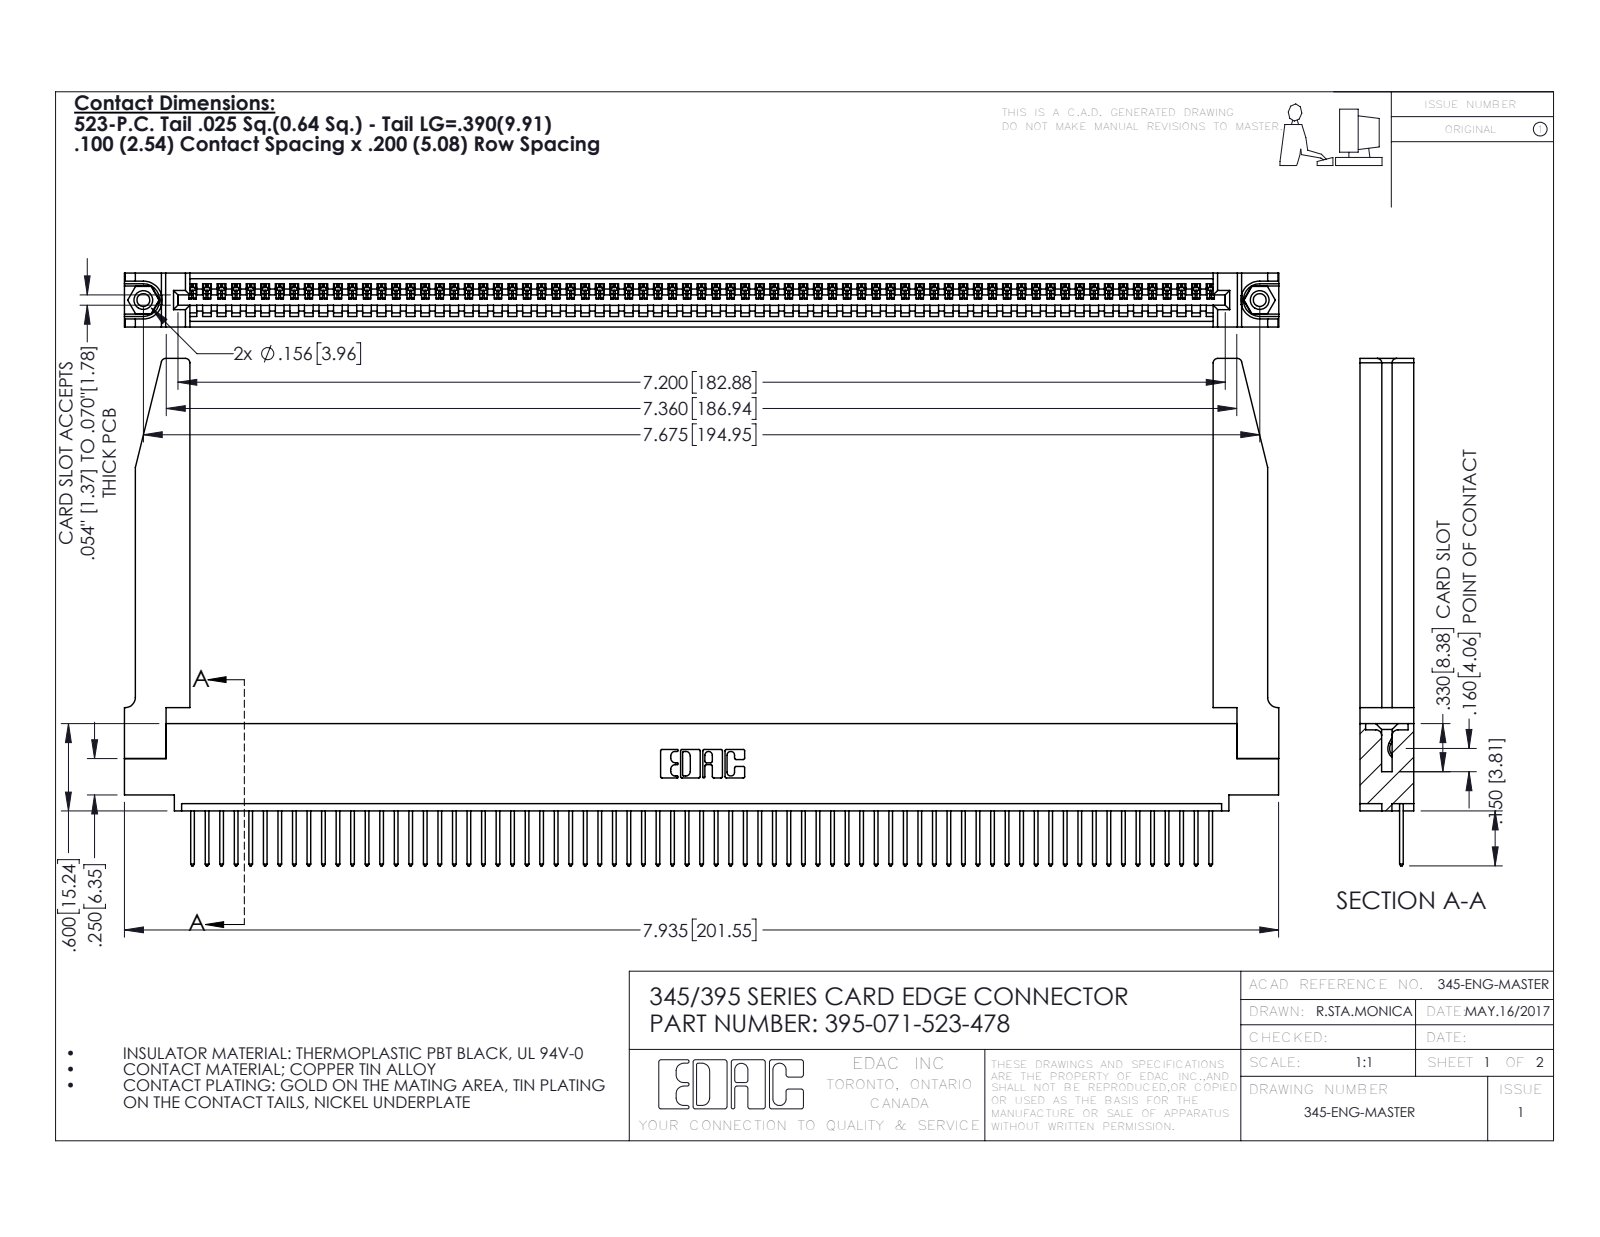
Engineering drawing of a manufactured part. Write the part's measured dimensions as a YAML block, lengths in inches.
part_name: "345-292-001_345-293-123; 395-071-523-478; 345-220-078_345-220-078; 345-250-001_345-250-001-102 (+1 more)"
step_written_by: "SolidWorks 2016 (CONFIG_CONTROL_DESIGN)"
units: inches
bodies: {solids: 76, faces: 4482, planar: 3066, cylindrical: 1364, other: 52}
overall_size: [7.936, 3.487, 0.37]
volume: 1.651
surface_area: 51.19
round_holes:
  - {diameter: 0.089, count: 2}
  - {diameter: 0.125, count: 2}
  - {diameter: 0.156, count: 2}
  - {diameter: 0.064, count: 1}
round_bosses_or_shafts:
  - {diameter: 0.155, count: 2}
partial_cylinders:
  - {radius: 0.006, count: 142}
  - {radius: 0.01, count: 142}
  - {radius: 0.01, count: 22}
  - {radius: 0.03, count: 8}
  - {radius: 0.007, count: 6}
  - {radius: 0.031, count: 6}
  - {radius: 0.026, count: 3}
  - {radius: 0.031, count: 2}
face_to_face_distances: [0.072, 0.298, 0.37, 0.098, 0.272, 0.025, 0.2, 0.225, 0.149, 0.148]
hole_center_spacings: [0.27, 7.439, 7.675]
